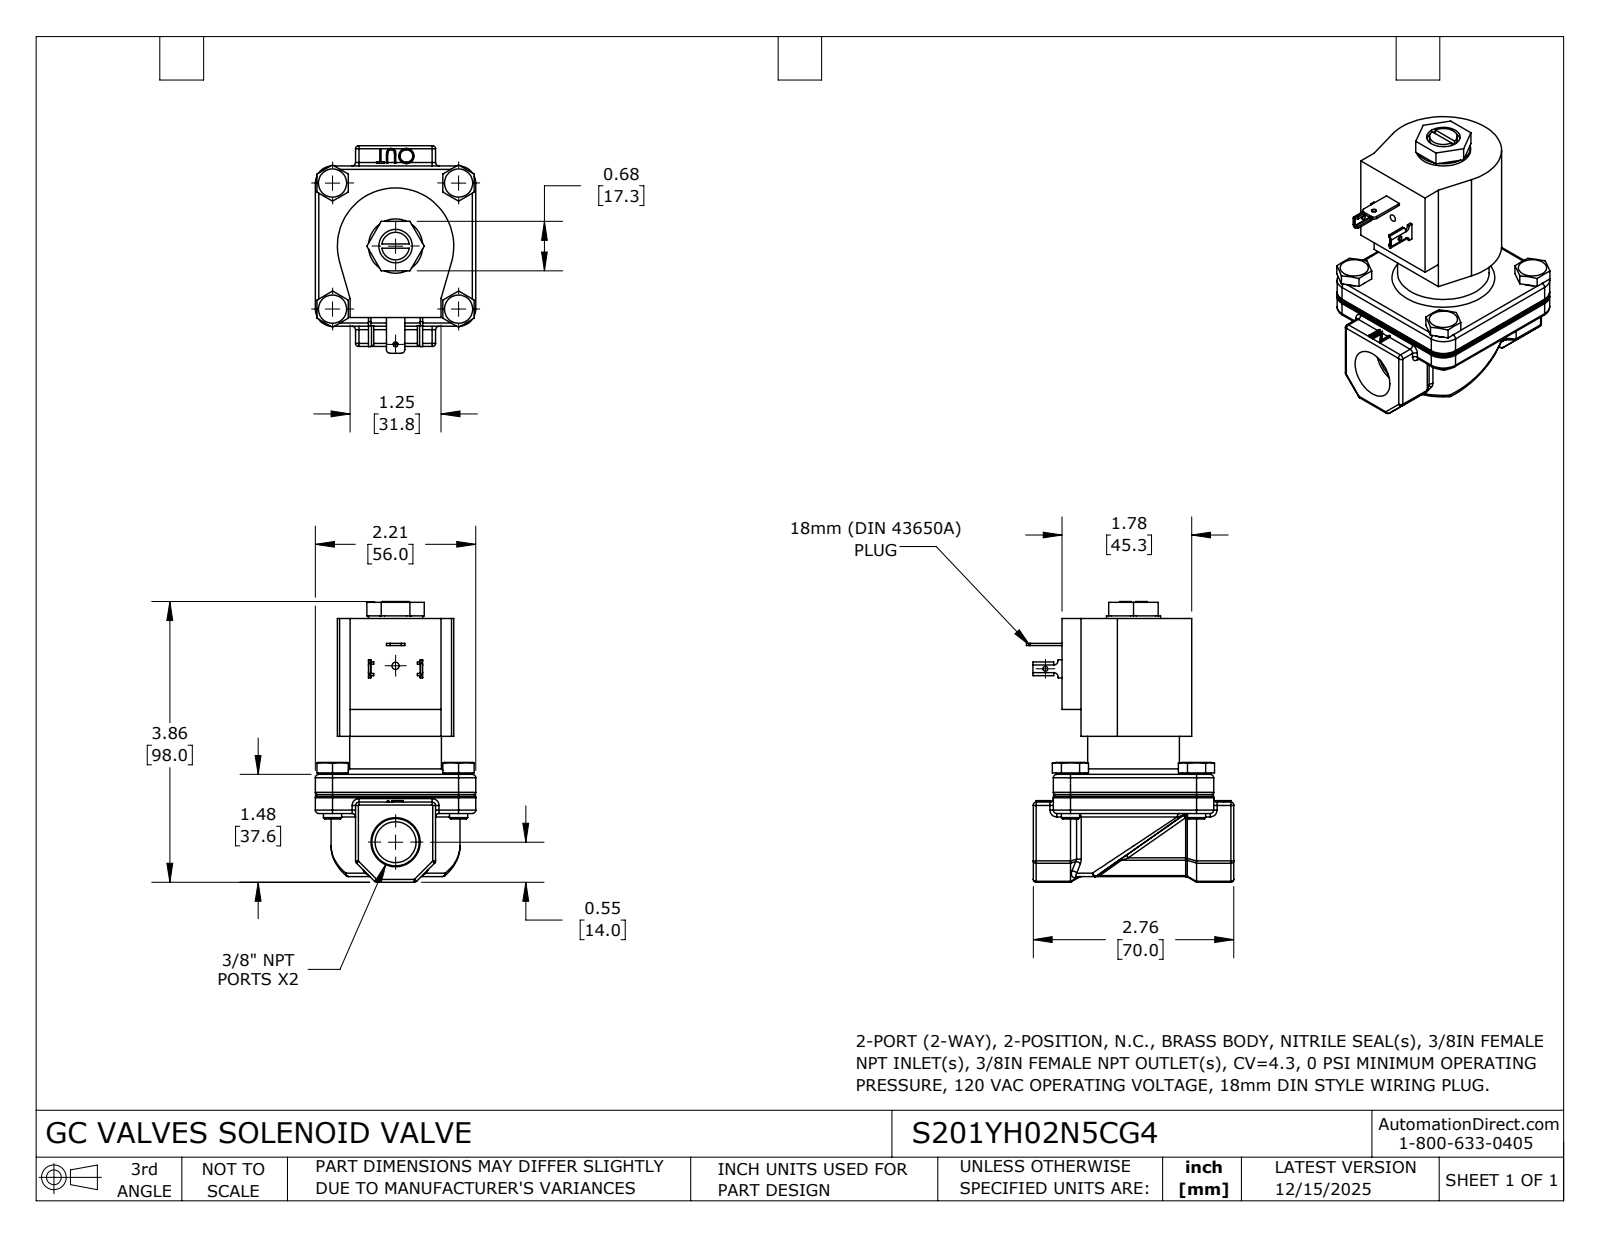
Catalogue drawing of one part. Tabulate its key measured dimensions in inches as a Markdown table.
| quantity | value |
| --- | --- |
| part name | S201YH02N5CG4 |
| STEP written by | SolidWorks 2024 (CONFIG_CONTROL_DESIGN) |
| units | inches |
| bodies | 1 solid, 483 faces (204 planar, 153 cylindrical, 126 other) |
| overall size | 3.857 × 2.851 × 2.205 |
| volume | 9.705 in³ |
| surface area | 40.43 in² |
| round holes (diameter × count) | 0.066 × 1, 0.067 × 1, 0.1 × 1, 0.46 × 1, 0.562 × 1 |
| round bosses / shafts (diameter × count) | 0.388 × 4, 0.25 × 4, 1.26 × 1, 0.746 × 1, 0.38 × 1 |
| partial cylindrical surfaces (radius × count) | 0.047 × 57, 0.04 × 12, 0.006 × 4, 0.031 × 4, 0.041 × 4, 0.234 × 4, 0.236 × 4, 0.05 × 2 |
| main face-to-face distances | 2.143, 0.551, 1.654, 2.205, 0.537, 2.68, 0.276, 2.48, 1.06, 0.523 |
| hole center spacings | 1.35, 2.423 |
